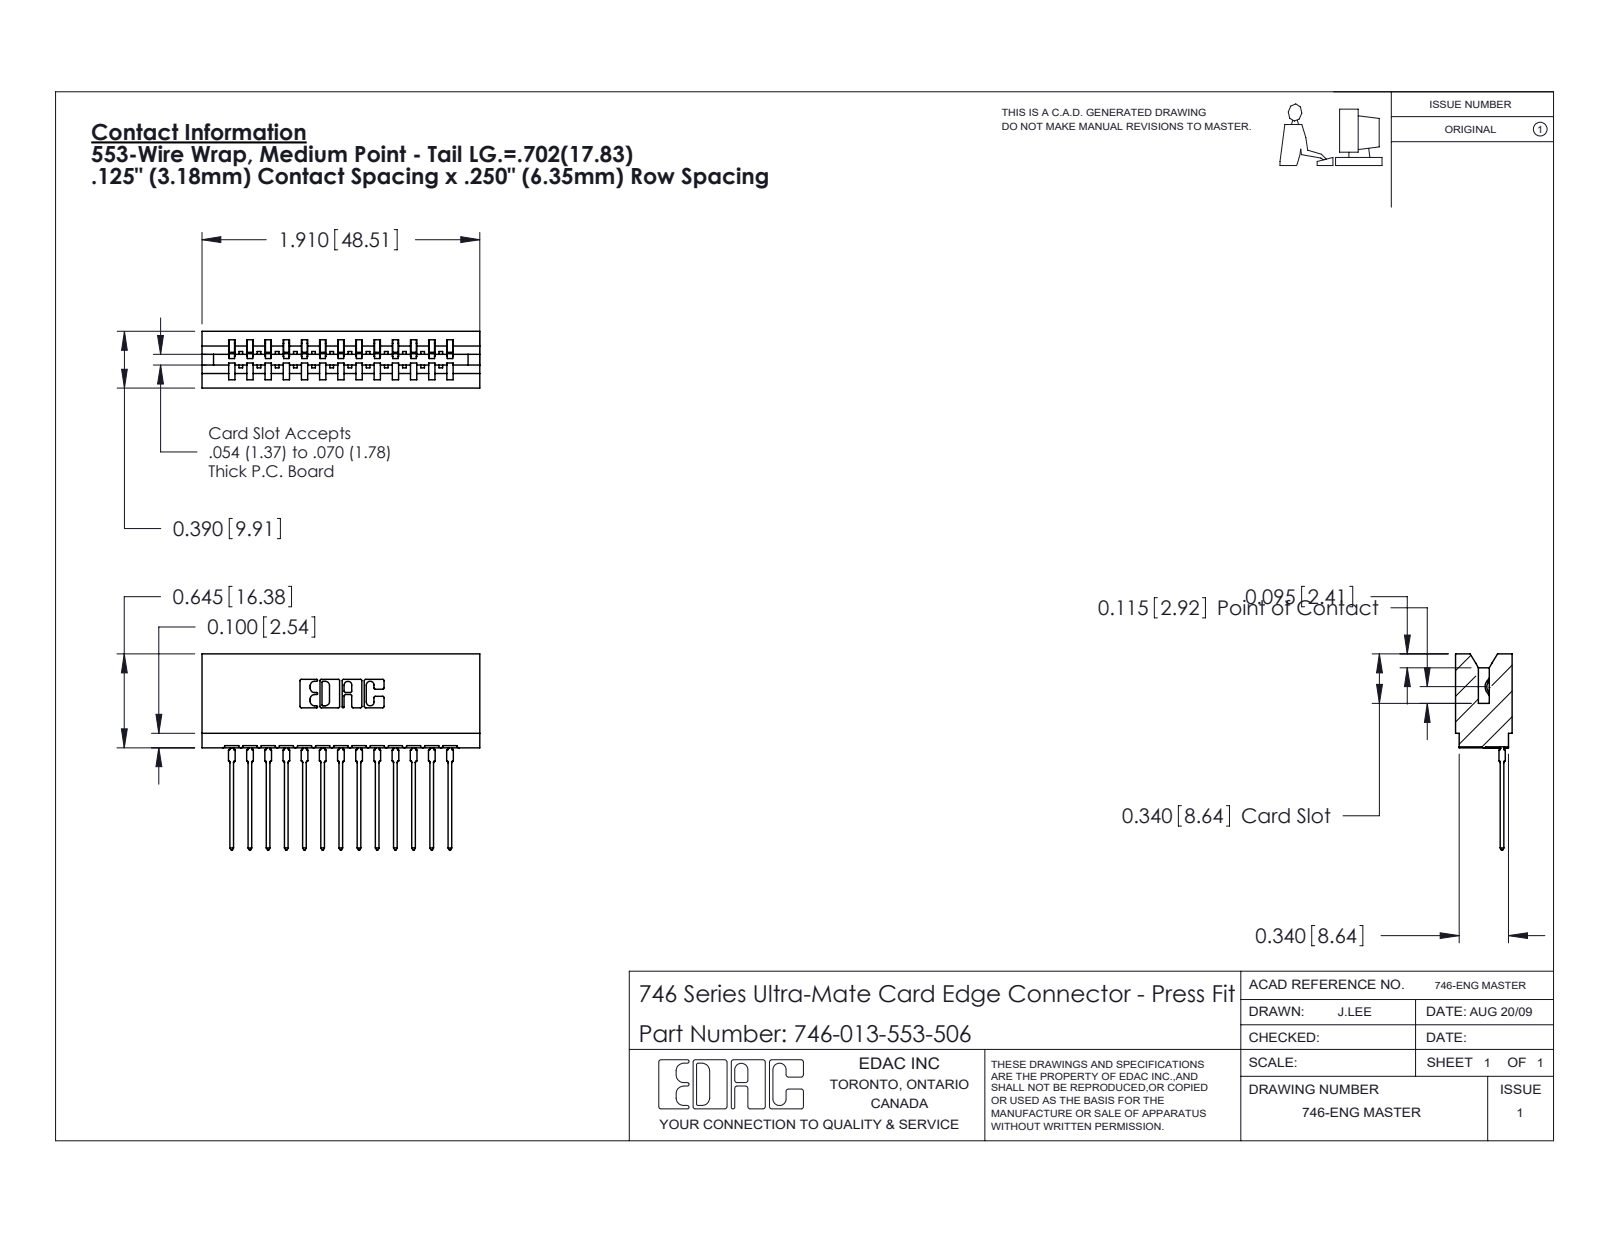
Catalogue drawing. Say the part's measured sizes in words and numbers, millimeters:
The part is named "746 Part_.340 Slot Depth - 06; 746-013-553-506; 746-292-001_553". Its 3-D file was written by "SolidWorks 2020 (CONFIG_CONTROL_DESIGN)". It is 14 solids with 1502 faces: 875 planar, 289 cylindrical and 338 other. Overall it measures 48.5 by 34.2 by 9.9 millimeters. Its volume is 5 650 cubic millimeters and its surface area 7 432 square millimeters. Partial cylindrical surfaces (rounded edges, fillets, slot ends): 26 of radius 0.5, 22 of radius 0.3, 14 of radius 0.4, 6 of radius 0.2, 6 of radius 0.8, 4 of radius 0.1, 4 of radius 0.3, 3 of radius 0.7. The main face-to-face distances are 6.4, 8.5, 1.4, 12.7, 3.2, 9.9, 7.4, 13.8, 19.1, 3.2.
